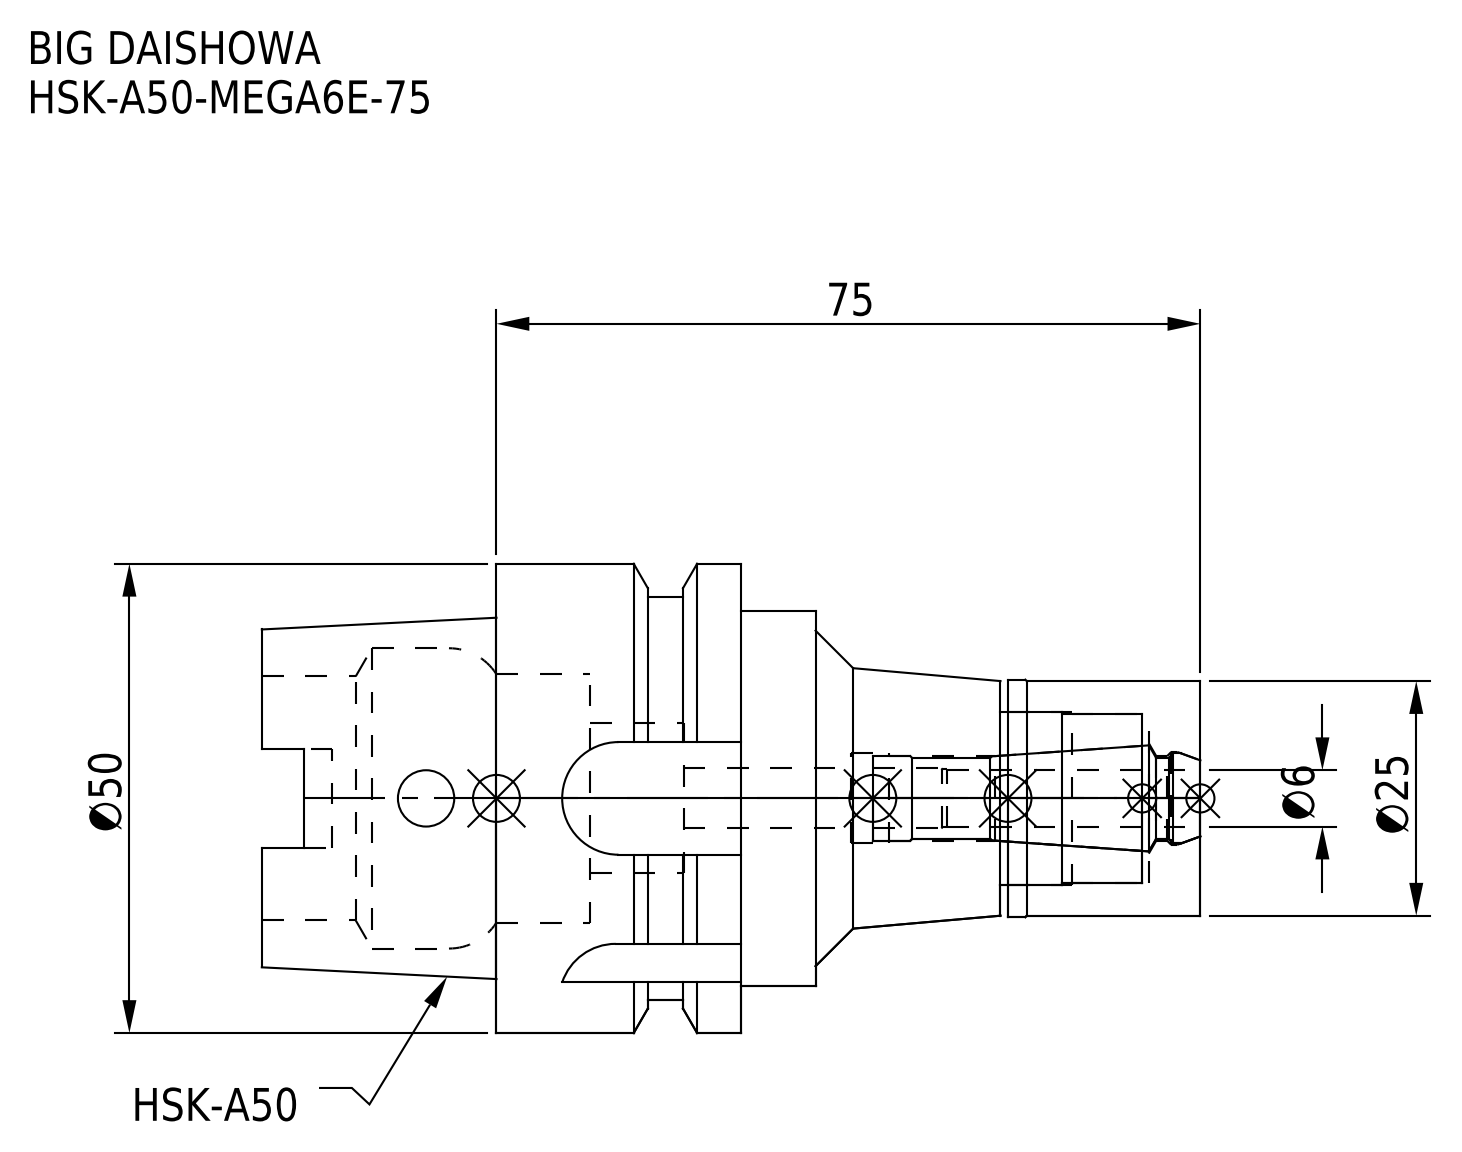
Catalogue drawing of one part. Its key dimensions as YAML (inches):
part_name: "DXF_TEMP_ASSY_ASM_4_ASM.stp; MEN6_1.stp; HSK-A50-MEGA6E-75-060.stp; HSK-A50-MEGA6E-75-060-FreeParts (+3 more)"
step_written_by: "SolidWorks 2019 (CONFIG_CONTROL_DESIGN)"
units: inches
bodies: {solids: 2, faces: 126, planar: 45, cylindrical: 53, other: 28}
overall_size: [3.937, 1.969, 1.969]
volume: 4.755
surface_area: 35.7
round_holes:
  - {diameter: 0.236, count: 1}
  - {diameter: 0.252, count: 1}
  - {diameter: 0.354, count: 1}
  - {diameter: 0.378, count: 1}
  - {diameter: 0.39, count: 1}
  - {diameter: 0.63, count: 1}
  - {diameter: 0.709, count: 1}
  - {diameter: 0.728, count: 1}
  - {diameter: 1.024, count: 1}
  - {diameter: 1.047, count: 1}
  - {diameter: 1.26, count: 1}
round_bosses_or_shafts:
  - {diameter: 1.969, count: 1}
  - {diameter: 1.693, count: 1}
  - {diameter: 1.575, count: 1}
  - {diameter: 0.996, count: 1}
  - {diameter: 0.984, count: 1}
partial_cylinders:
  - {radius: 0.094, count: 4}
  - {radius: 0.236, count: 4}
face_to_face_distances: [1.024, 0.807, 2.953, 1.929, 2.561, 0.632, 0.392, 2.146, 3.937, 2.008]
